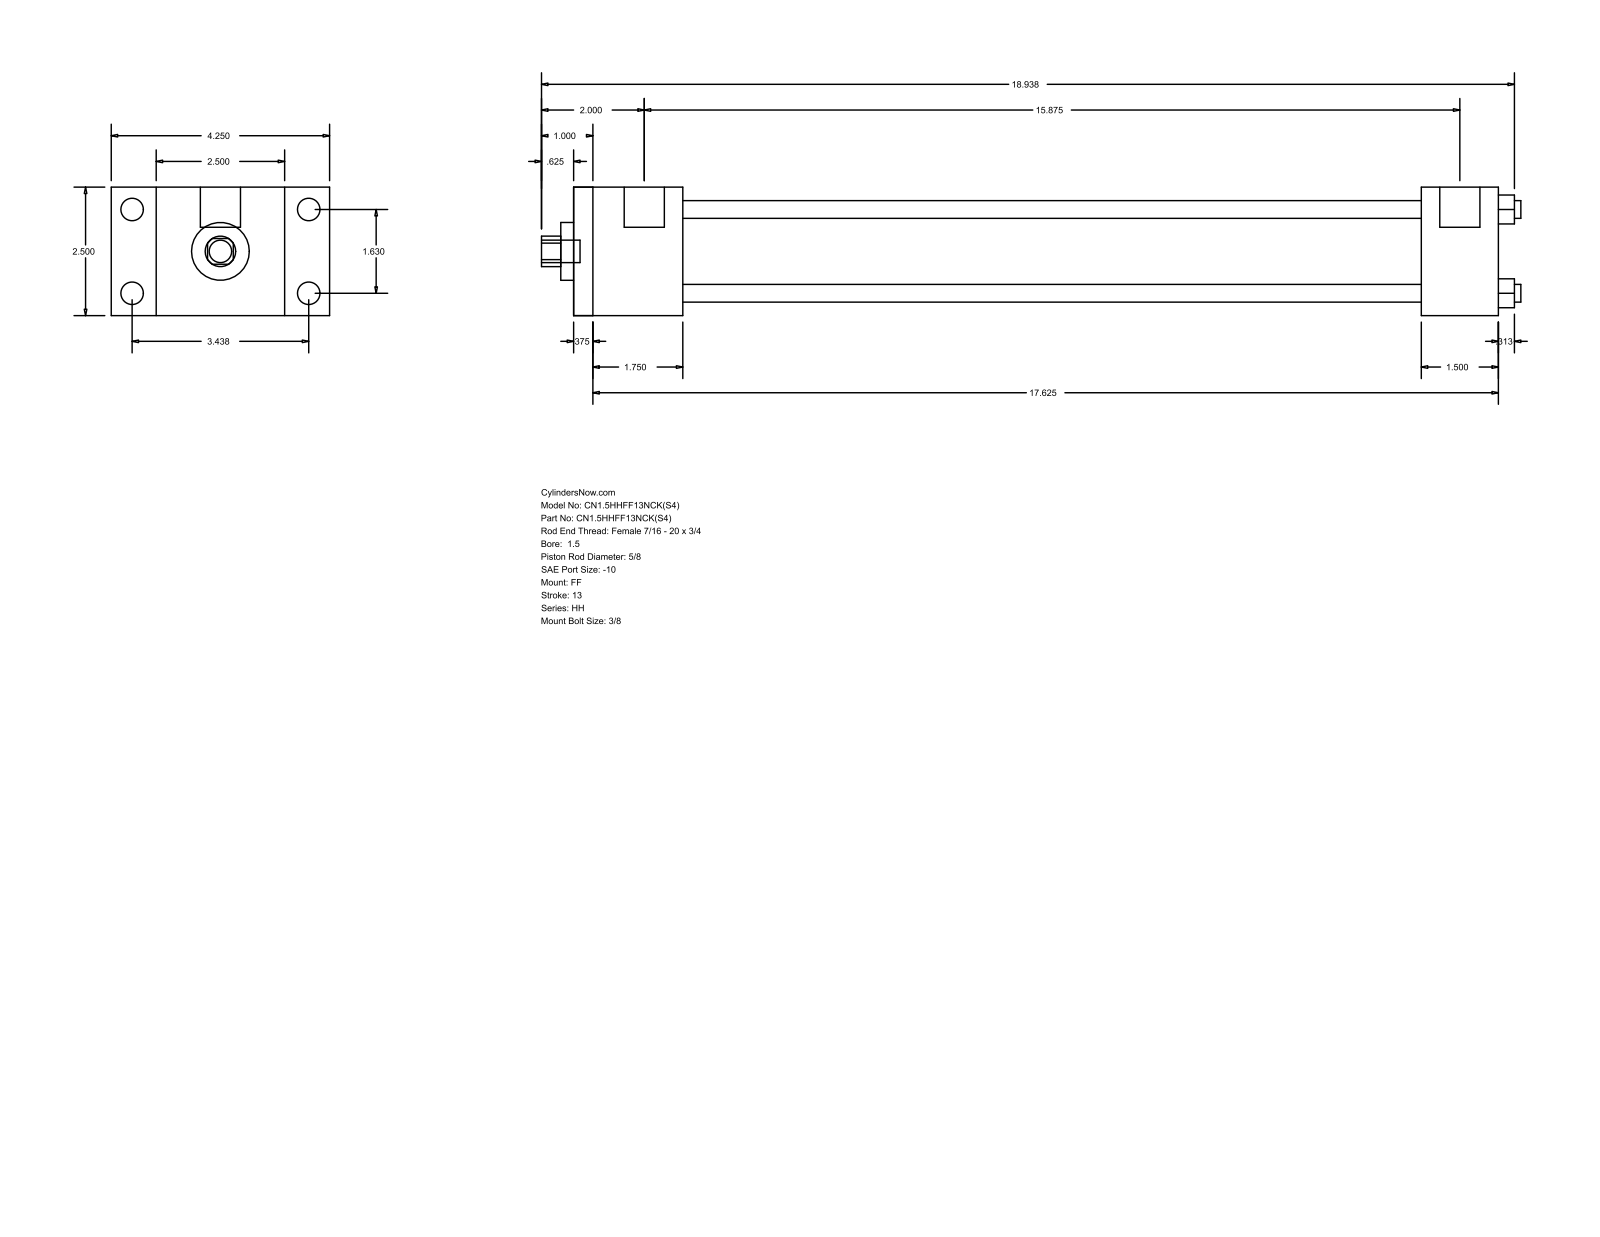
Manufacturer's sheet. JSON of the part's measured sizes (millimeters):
{"part_name": "HH_FF__0150_0.625", "step_written_by": "GSSL Pune (CONFIG_CONTROL_DESIGN)", "units": "millimeters", "bodies": {"solids": 0, "faces": 92, "planar": 64, "cylindrical": 28, "other": 0}, "overall_size": [484.19, 107.95, 63.5], "round_holes": [[8.76, 4], [15.88, 1], [28.57, 1], [44.45, 1]], "round_bosses_or_shafts": [[11.13, 4], [5.56, 4], [19.84, 2], [11.11, 1]], "partial_cylinders_radius": [[7.54, 1]], "face_to_face_distances": [63.5, 457.19, 9.52, 447.67, 53.97, 44.45, 403.22, 419.1, 409.58, 365.13], "hole_center_spacings": [29.27, 41.4, 58.55]}
